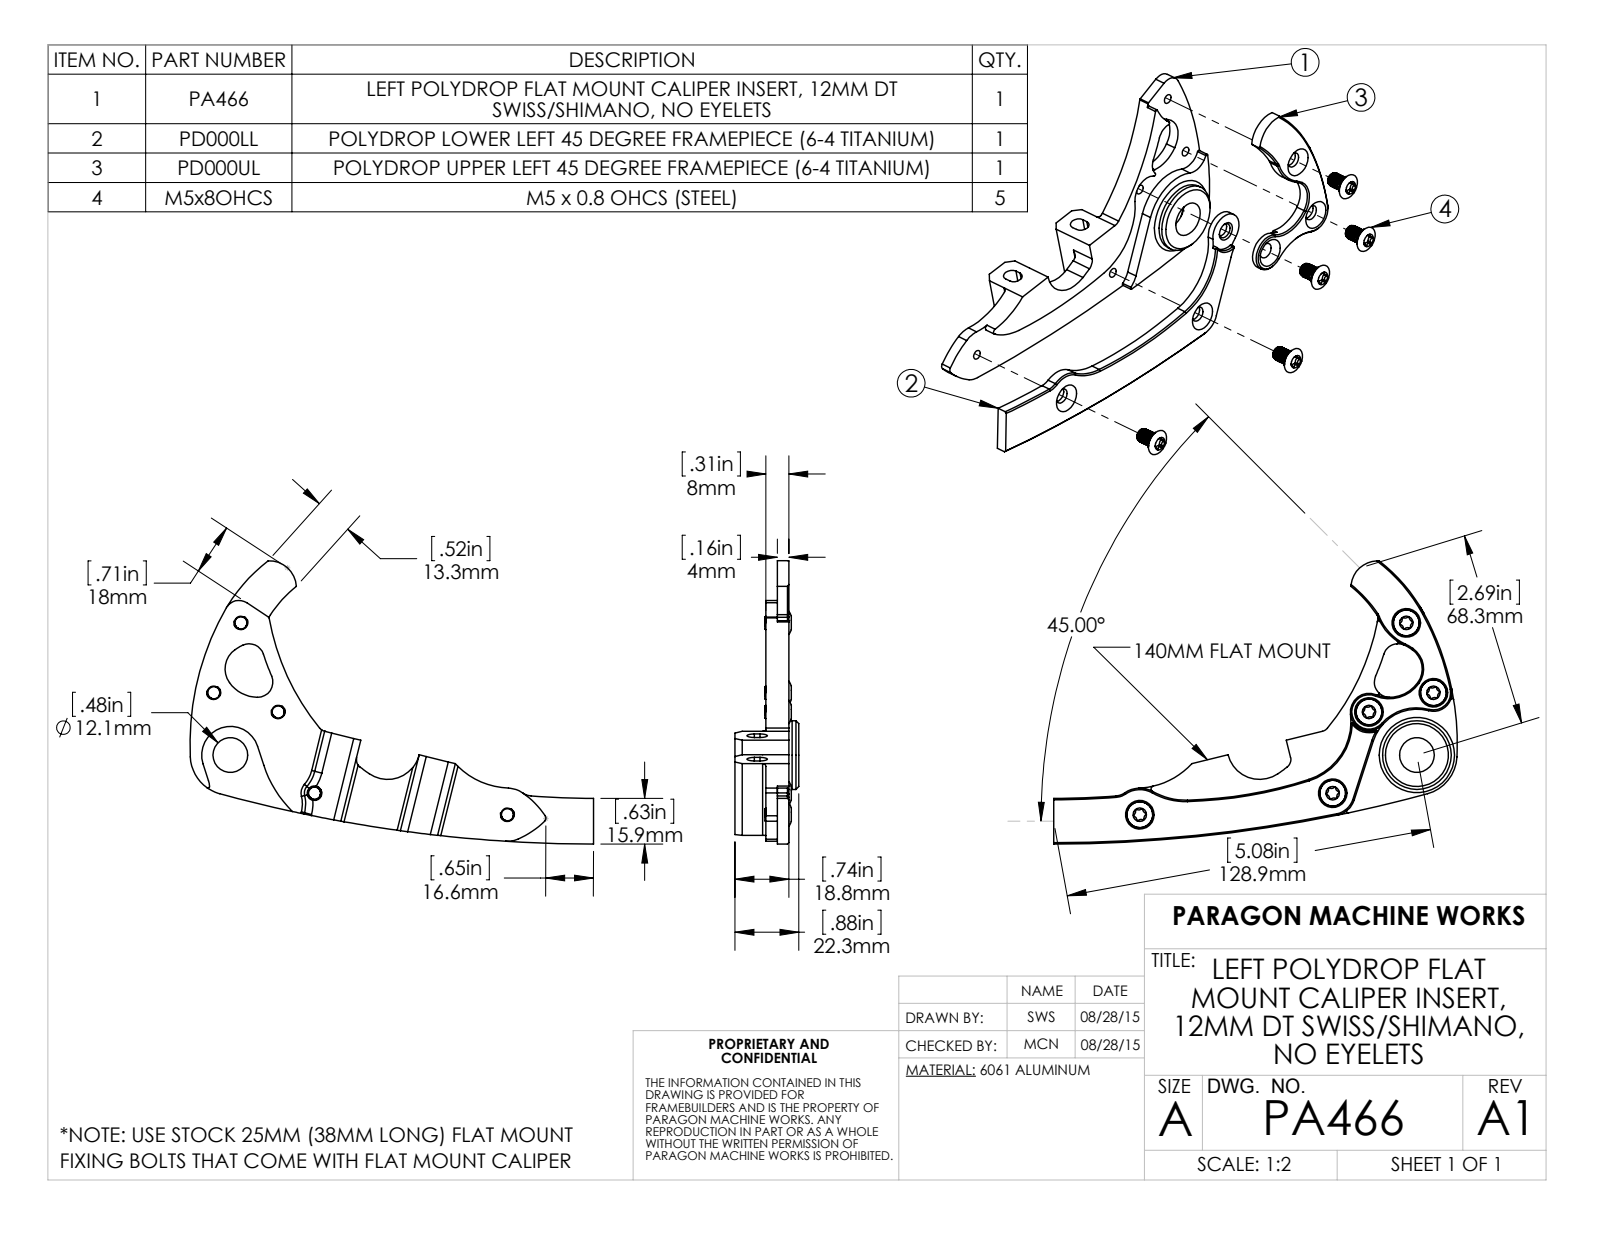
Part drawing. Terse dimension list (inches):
name: PA466
written by: SolidWorks 2015 (AUTOMOTIVE_DESIGN)
unit: in
bodies: 1 solid, 181 faces (41 planar, 80 cylindrical, 60 other)
size: 4.894 × 3.311 × 0.879
volume: 1.597 in³; area: 21.11 in²
holes: 5× ⌀0.13, 1× ⌀0.477
bosses: 1× ⌀0.945
rounds: 7× R0.02, 5× R0.045, 4× R0.102, 4× R0.217, 2× R0.13, 2× R0.256, 2× R0.5, 2× R1.209
face distances: 0.157, 0.315, 0.138, 0.741, 0.584, 0.426, 0.177, 0.02, 0.564, 0.295
hole spacings: 0.886, 0.924, 1.03, 1.223, 1.271, 1.327, 1.822, 1.956
